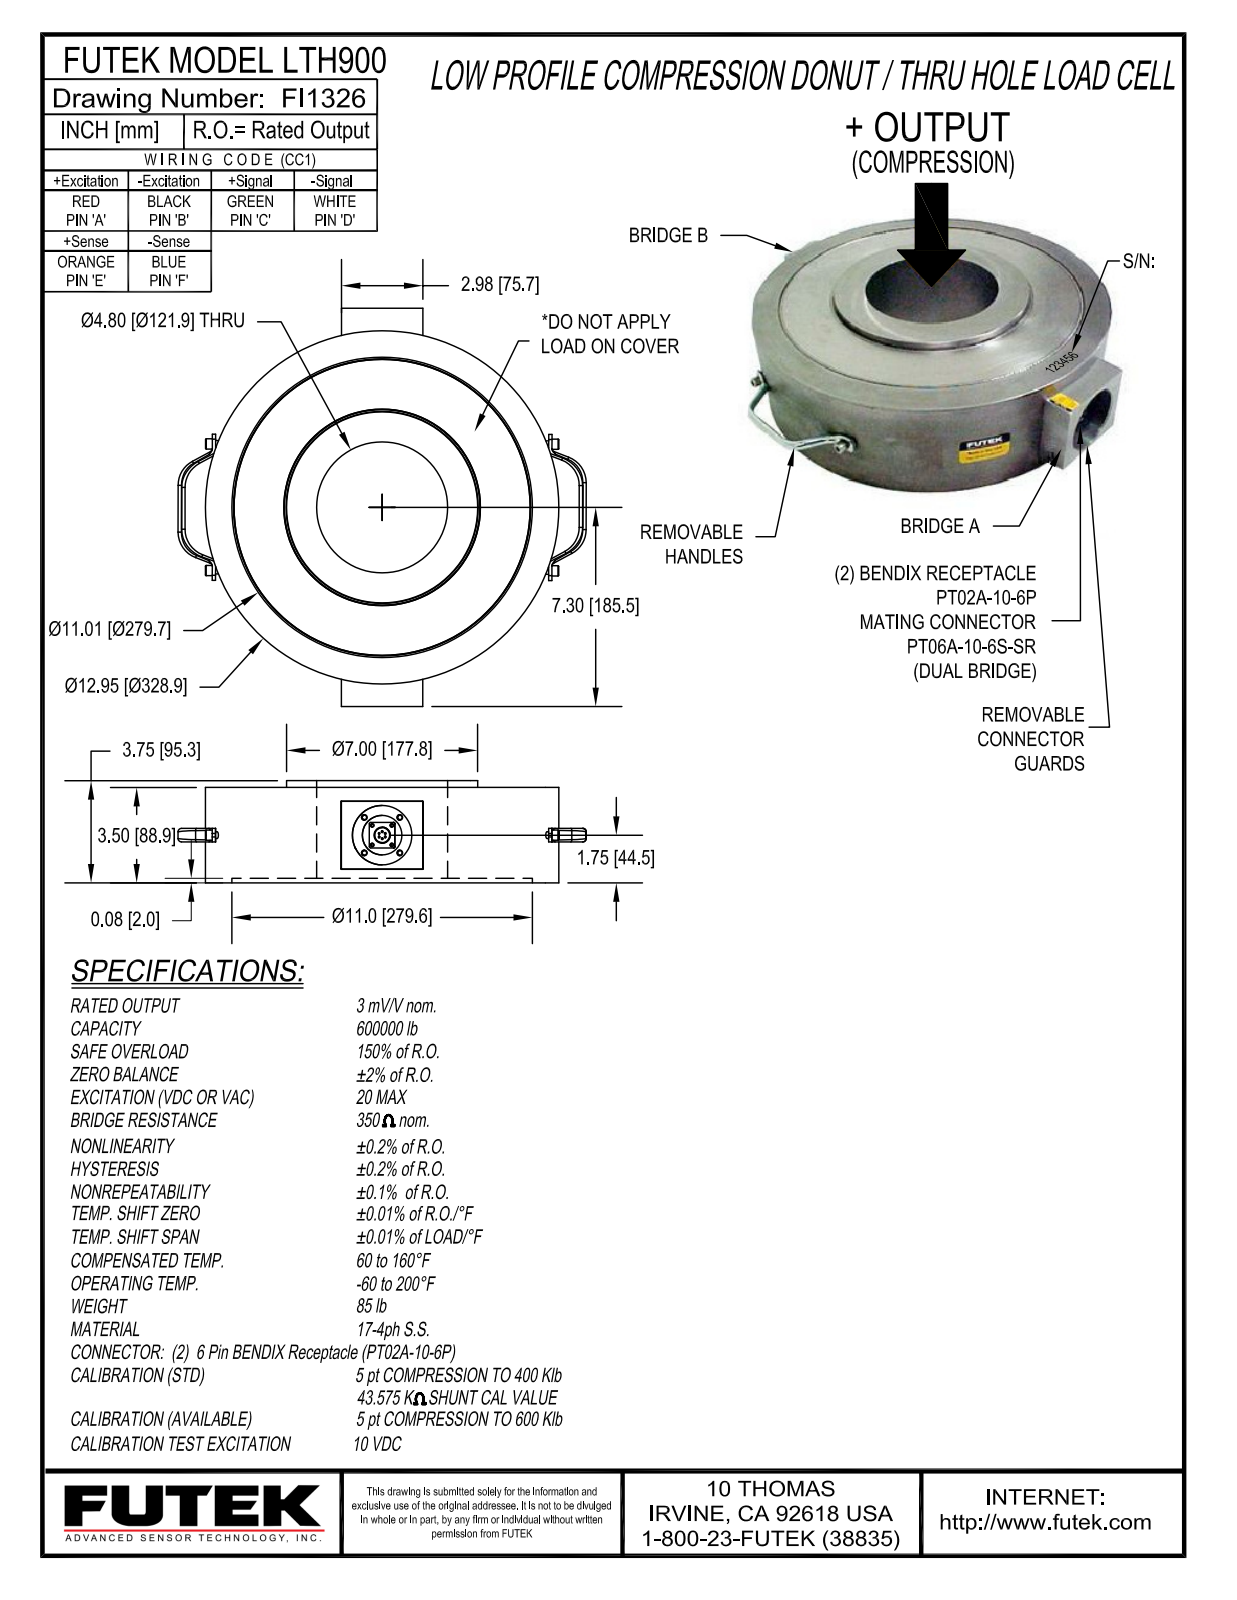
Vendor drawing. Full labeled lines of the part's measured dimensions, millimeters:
Part name (STEP PRODUCT): LTH900
STEP written by: Autodesk Inventor 2008 (AUTOMOTIVE_DESIGN)
Units: millimetres
Bodies: 1 solid, 672 faces (321 planar, 183 cylindrical, 168 other)
Overall size (bounding box): 379.8 × 370.9 × 95.3
Volume: 6 566 000 mm³ · Surface area: 339 000 mm²
Round holes (diameter × count): ⌀2.4 ×8, ⌀3.3 ×8, ⌀4.2 ×8, ⌀5.2 ×8, ⌀5.6 ×7, ⌀3.5 ×2, ⌀9.5 ×2, ⌀14 ×2, ⌀15.9 ×2, ⌀36.8 ×2, ⌀55.3 ×2, ⌀121.9 ×1
Round bosses / shafts (diameter × count): ⌀1.5 ×24, ⌀7.9 ×8, ⌀4.8 ×8, ⌀4.6 ×8, ⌀2.8 ×8, ⌀9.5 ×4, ⌀6.4 ×4, ⌀15 ×2
Partial cylindrical surfaces — rounded edges, fillets, slot ends (radius × count): R1.3 ×8, R4.7 ×8, R25.4 ×8, R3.2 ×4
Main face-to-face distances: 85.6, 85.8, 3.1, 88.7, 88.9, 2, 1.1, 86.7, 86.9, 6.4
Hole centre spacings: 33, 26.7, 18.3, 10.4, 23.4, 12.9, 12.9, 12.9
